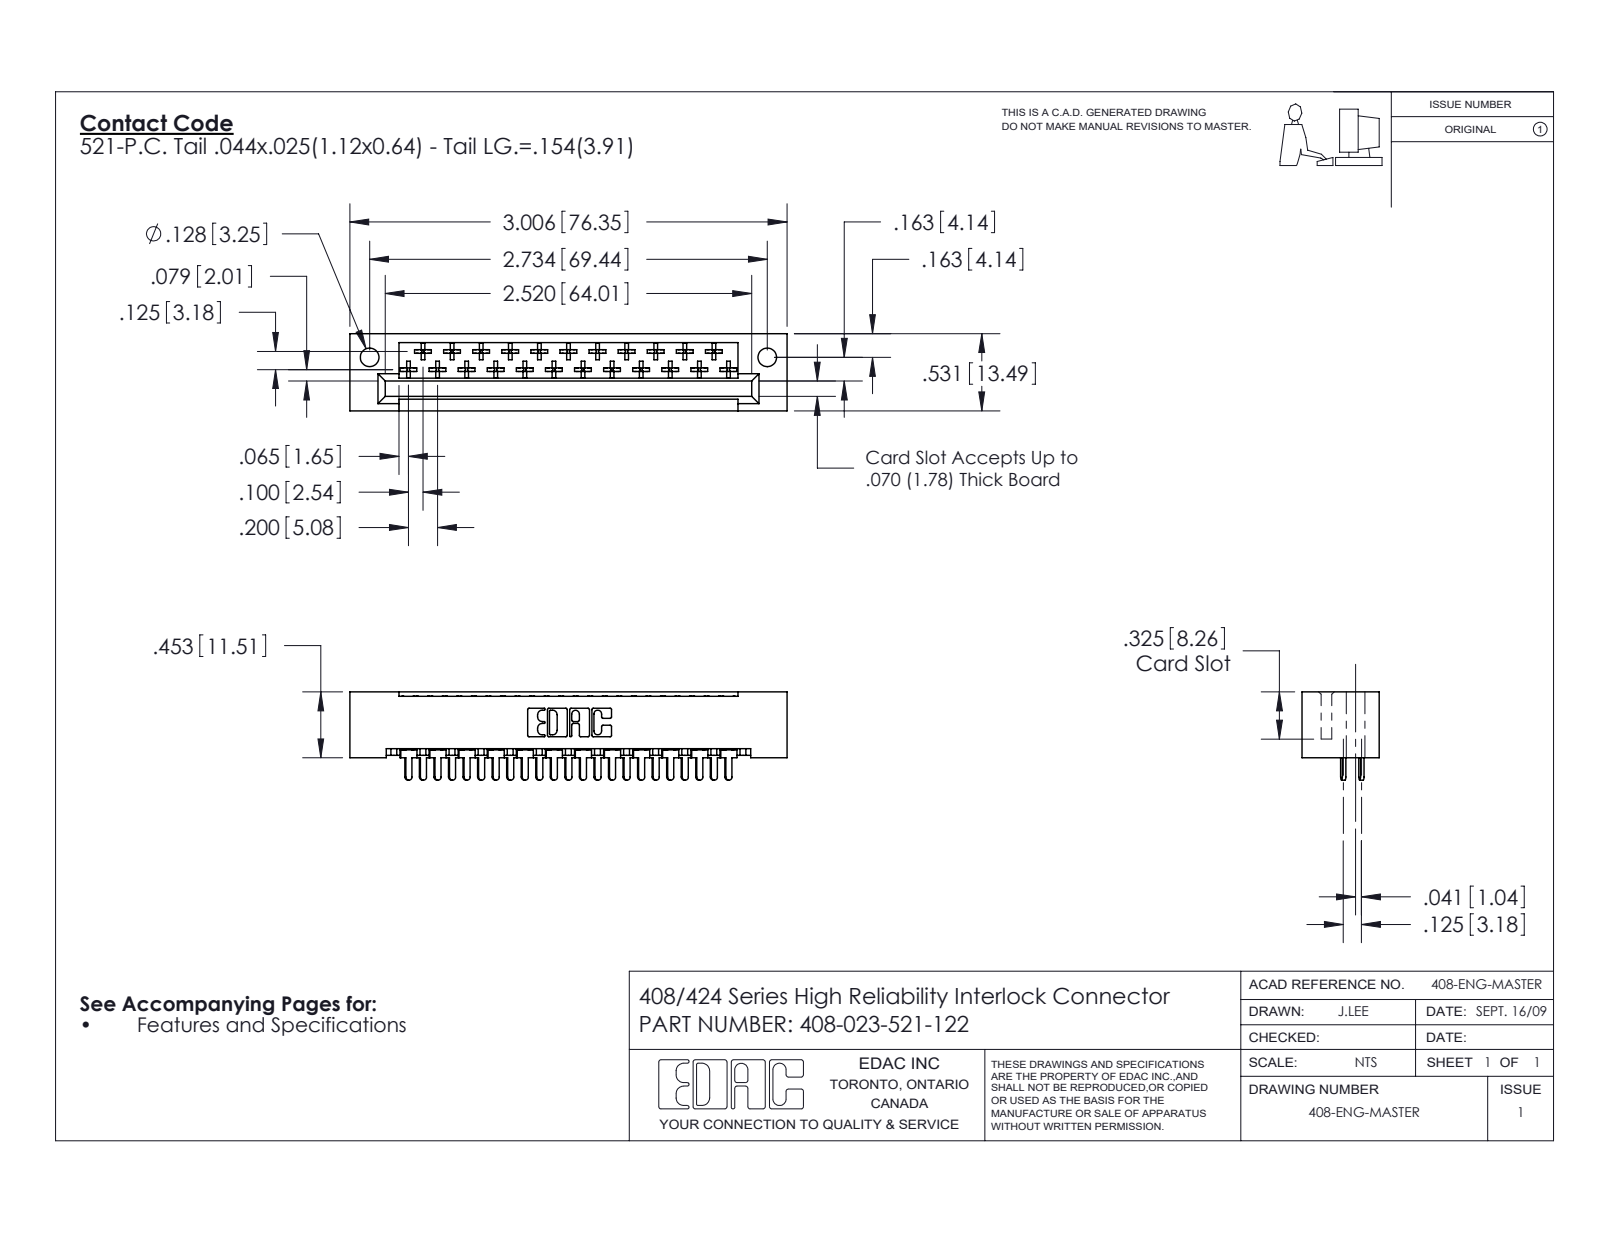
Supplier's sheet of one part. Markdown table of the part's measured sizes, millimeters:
| quantity | value |
| --- | --- |
| part name | 408-023-521-122; 408 Part_023 - 1; 408-290-001_408-290-121 |
| STEP written by | SolidWorks 2016 (CONFIG_CONTROL_DESIGN) |
| units | millimeters |
| bodies | 24 solids, 1392 faces (1045 planar, 255 cylindrical, 92 other) |
| overall size | 76.4 × 15.4 × 13.5 |
| volume | 8 470 mm³ |
| surface area | 10 100 mm² |
| round holes (diameter × count) | 3.3 × 2 |
| partial cylindrical surfaces (radius × count) | 0.3 × 138, 0.5 × 25, 0.6 × 23, 0.3 × 22, 0.2 × 6, 0.8 × 6, 0.7 × 3 |
| main face-to-face distances | 2.5, 7.5, 13.5, 0.6, 3.2, 0.6, 6.9, 6, 6.6, 5.5 |
| hole center spacings | 69.4 |
